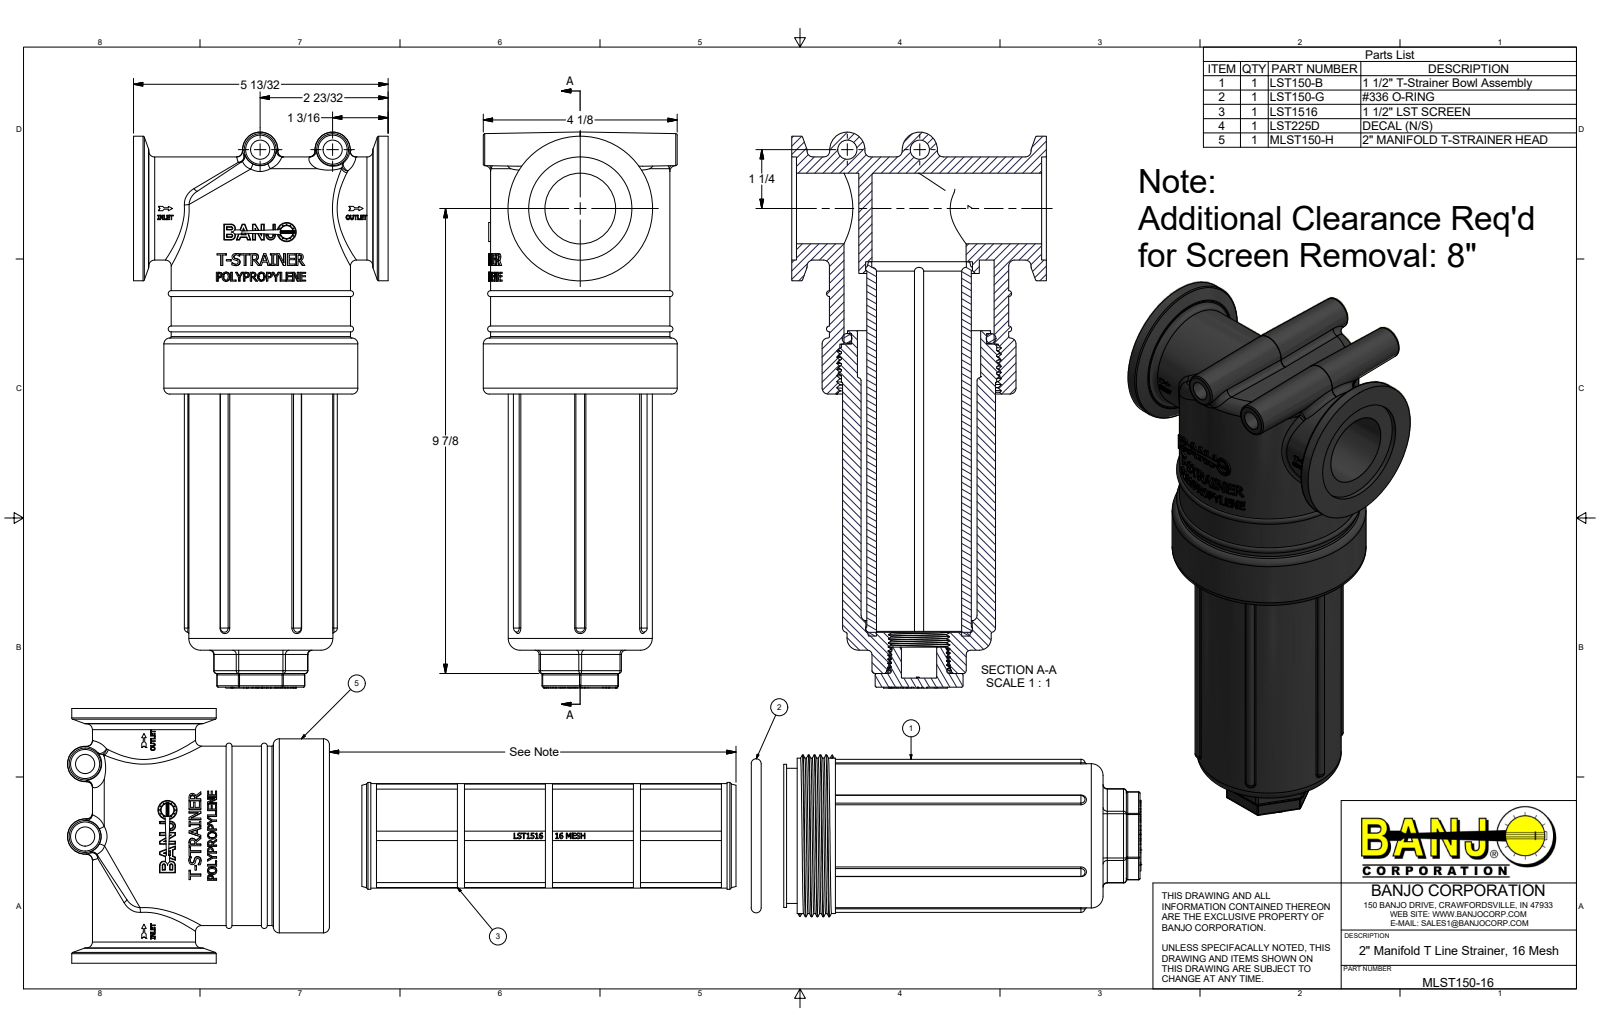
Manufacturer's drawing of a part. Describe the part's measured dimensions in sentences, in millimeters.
The part is named "MLST150-H; LST150-XB; LSQ200-R; LSQ200-PL (+4 more)". Its 3-D file was written by "Autodesk Inventor 2015 (AUTOMOTIVE_DESIGN)". It is 30 solids with 1870 faces: 987 planar, 255 cylindrical and 628 other. Overall it measures 299.97 by 138.18 by 104.65 millimeters. Its volume is 841 801 cubic millimeters and its surface area 323 924 square millimeters. Round holes: 2 of diameter 10.32, 1 of diameter 6.92, 1 of diameter 9.77, 1 of diameter 19.05, 1 of diameter 38.1, 1 of diameter 45.97, 1 of diameter 50.04, 1 of diameter 50.8, 1 of diameter 57.4, 1 of diameter 66.55, 1 of diameter 81.03, 1 of diameter 85.46. Round bosses or shafts: 1 of diameter 104.65, 1 of diameter 87.26, 1 of diameter 83.82, 1 of diameter 77.98, 1 of diameter 77.79, 1 of diameter 77.22, 1 of diameter 72.9, 1 of diameter 65.02. Partial cylindrical surfaces (rounded edges, fillets, slot ends): 42 of radius 0.76, 13 of radius 1.52, 6 of radius 1.98, 6 of radius 2.29, 6 of radius 2.38, 5 of radius 2.54, 2 of radius 0.6, 2 of radius 0.86. The main face-to-face distances are 2.54, 135.64, 138.18, 31.49, 92.2, 23.37, 155.45, 247.65, 66.55, 71.63. The hole center spacings are 39.11, 46.81, 50.73.
